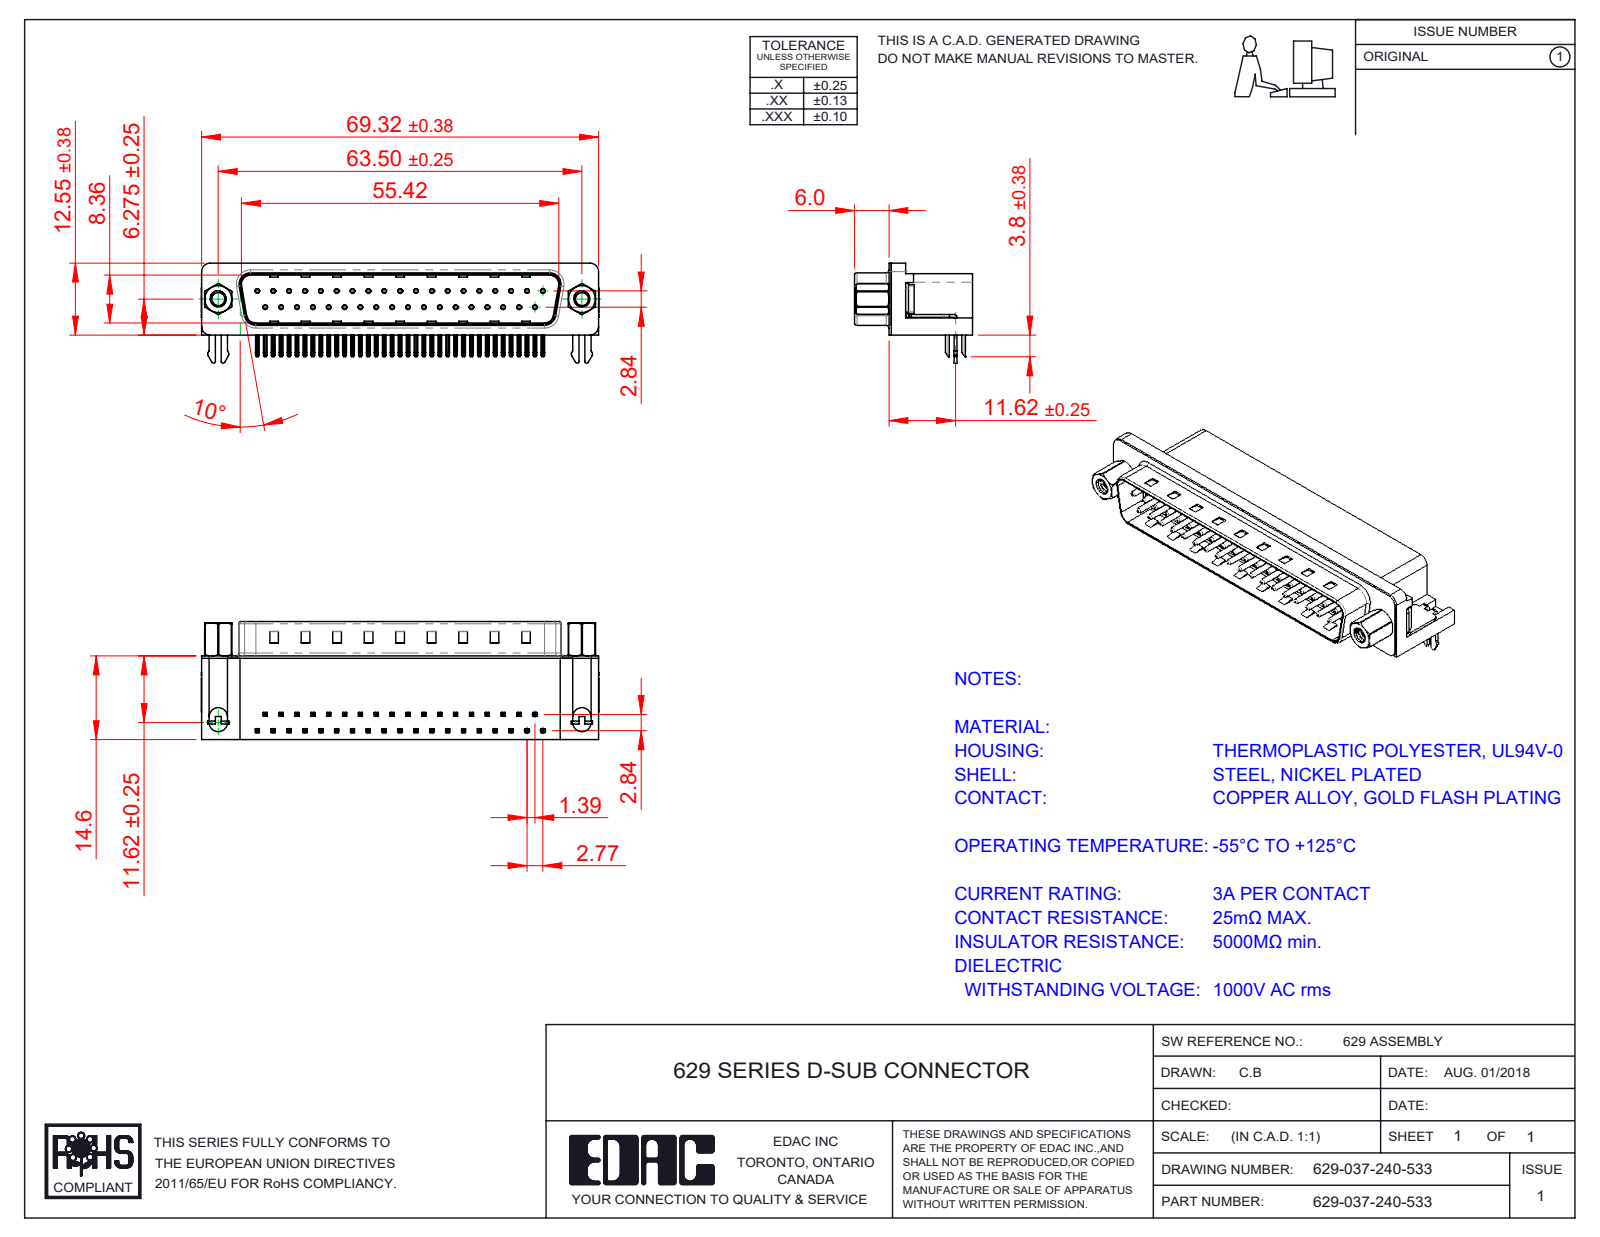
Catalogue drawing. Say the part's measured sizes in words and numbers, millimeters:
The part is named "629 Housing_37 Socket; 629 4-40 Hex Standoff 5; 629 2 Prong Board Lock; 629 Contact Top (+4 more)". Its 3-D file was written by "SolidWorks 2020 (CONFIG_CONTROL_DESIGN)". It is 45 solids with 3363 faces: 2065 planar, 995 cylindrical and 303 other. Overall it measures 69.4 by 20.6 by 17.48 millimeters. Its volume is 10 183 cubic millimeters and its surface area 11 314 square millimeters. Round holes: 37 of diameter 0.35, 37 of diameter 0.8, 2 of diameter 2.26, 2 of diameter 2.29, 2 of diameter 4, 2 of diameter 4.8, 2 of diameter 5. Round bosses or shafts: 37 of diameter 0.75, 2 of diameter 4.9, 2 of diameter 4.75, 2 of diameter 3.9, 2 of diameter 2.79. Partial cylindrical surfaces (rounded edges, fillets, slot ends): 156 of radius 0.25, 74 of radius 0.12, 16 of radius 1, 14 of radius 0.5, 8 of radius 1.6, 7 of radius 1.5, 4 of radius 0.32, 4 of radius 0.9. The main face-to-face distances are 0.4, 10.35, 14.2, 8.76, 1.7, 2.1, 10.46, 10.86, 14.6, 1.35. The hole center spacings are 2.77, 3.16, 5.54, 8.31, 11.08, 13.85, 16.62, 19.39.
